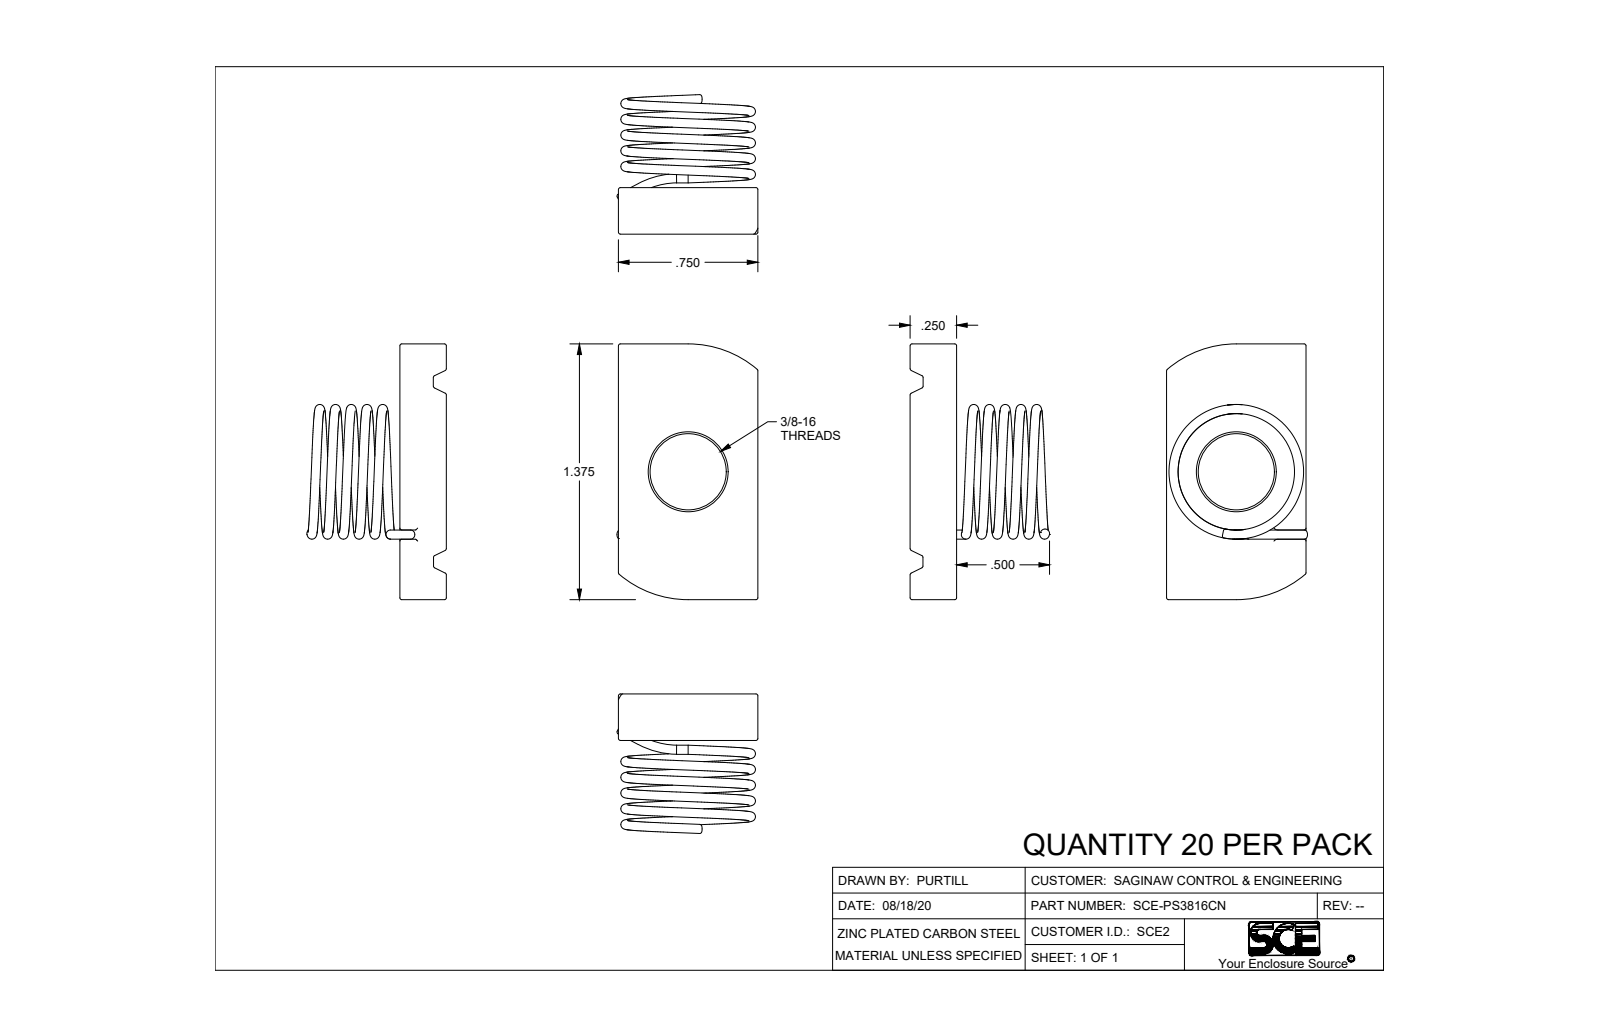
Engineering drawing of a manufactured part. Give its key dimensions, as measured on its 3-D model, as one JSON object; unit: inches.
{"part_name": "SCE-PS3816CN", "step_written_by": "SolidWorks 2019 (CONFIG_CONTROL_DESIGN)", "units": "inches", "bodies": {"solids": 1, "faces": 115, "planar": 19, "cylindrical": 50, "other": 46}, "overall_size": [1.375, 0.758, 0.75], "volume_in3": 0.227, "surface_area_in2": 4.822, "round_holes": [[0.41, 1]], "round_bosses_or_shafts": [[0.049, 2]], "partial_cylinders_radius": [[0.01, 38], [0.572, 2]], "face_to_face_distances": [0.25, 0.75, 1.375, 0.181, 0.069, 0.18, 0.07, 0.325, 1.05, 0.375]}
